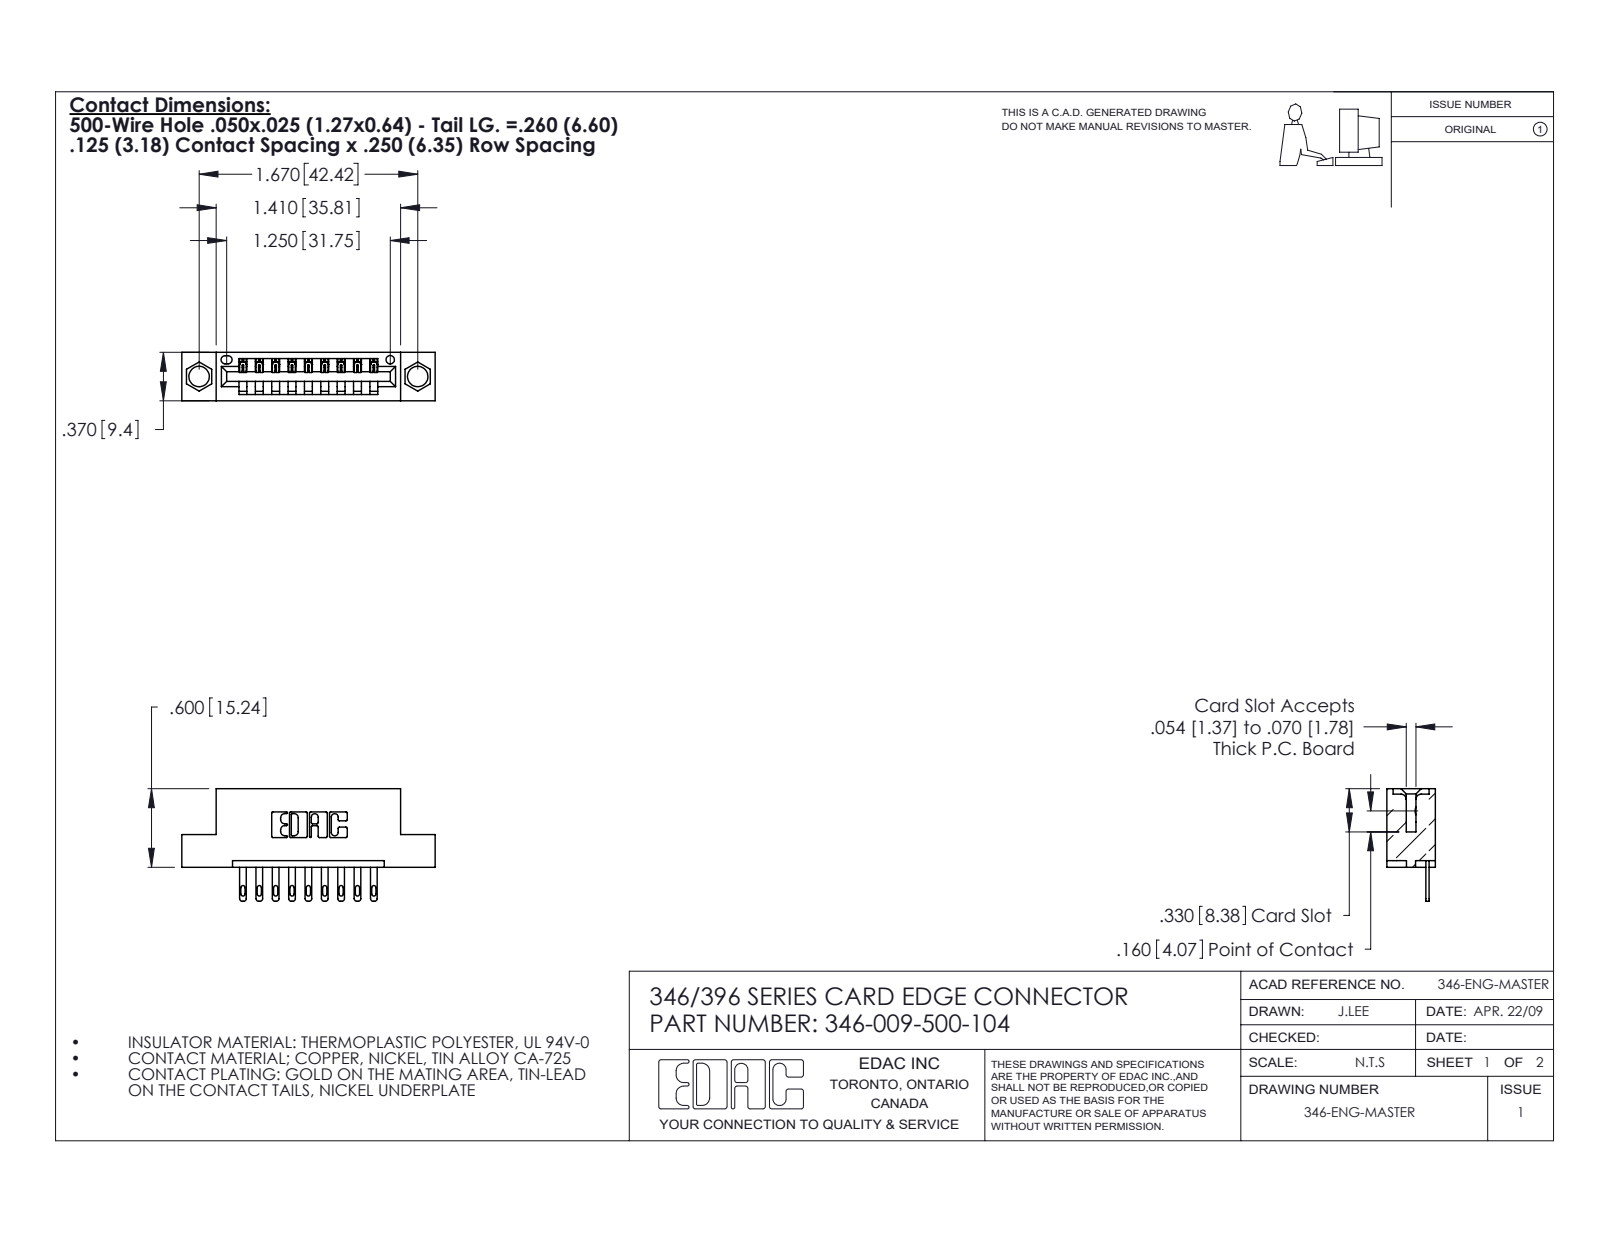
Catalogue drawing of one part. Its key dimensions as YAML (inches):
part_name: "346 Part_Flush Mounting Lugs - 0.156 Dia-TH; 346-009-500-104; 345-292-001_345-293-100"
step_written_by: "SolidWorks 2020 (CONFIG_CONTROL_DESIGN)"
units: inches
bodies: {solids: 10, faces: 622, planar: 396, cylindrical: 226, other: 0}
overall_size: [1.935, 0.86, 0.37]
volume: 0.267
surface_area: 7.708
round_holes:
  - {diameter: 0.156, count: 2}
  - {diameter: 0.064, count: 1}
partial_cylinders:
  - {radius: 0.01, count: 22}
  - {radius: 0.006, count: 18}
  - {radius: 0.016, count: 18}
  - {radius: 0.02, count: 18}
  - {radius: 0.007, count: 6}
  - {radius: 0.031, count: 6}
  - {radius: 0.026, count: 3}
  - {radius: 0.031, count: 2}
face_to_face_distances: [0.25, 0.048, 0.322, 0.37, 0.072, 0.298, 0.025, 0.148, 0.222, 0.1]
hole_center_spacings: [0.246, 1.465, 1.67]
